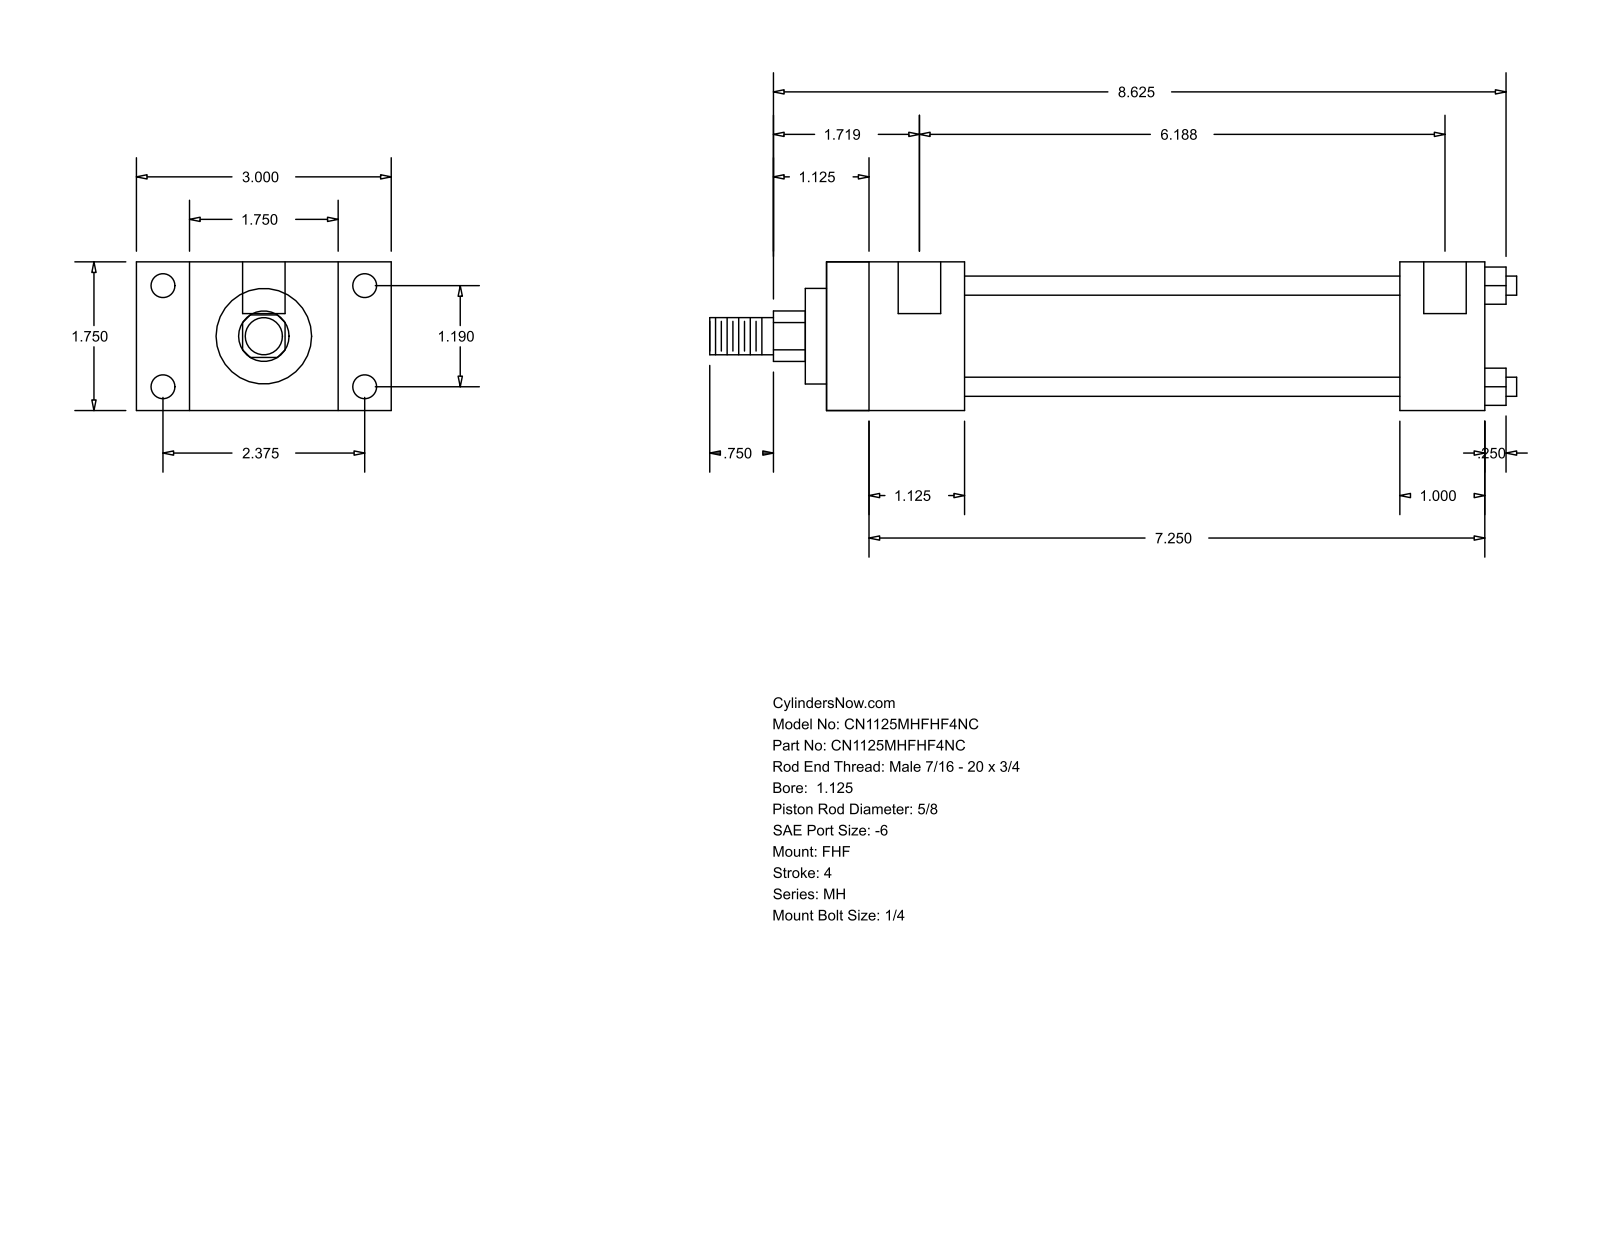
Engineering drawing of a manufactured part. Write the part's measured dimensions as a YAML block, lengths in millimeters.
part_name: "MH_FHF__0112_0.625"
step_written_by: "GSSL Pune (CONFIG_CONTROL_DESIGN)"
units: millimeters
bodies: {solids: 0, faces: 88, planar: 60, cylindrical: 28, other: 0}
overall_size: [241.3, 76.2, 44.45]
round_holes:
  - {diameter: 5.56, count: 4}
  - {diameter: 7.14, count: 4}
  - {diameter: 12.7, count: 2}
round_bosses_or_shafts:
  - {diameter: 5.71, count: 4}
  - {diameter: 34.92, count: 1}
  - {diameter: 28.57, count: 1}
  - {diameter: 15.88, count: 1}
  - {diameter: 11.11, count: 1}
partial_cylinders:
  - {radius: 7.54, count: 1}
face_to_face_distances: [44.46, 15.87, 60.33, 41.27, 76.2, 196.84, 155.57, 25.4, 171.44, 130.17]
hole_center_spacings: [30.22, 60.32, 67.47, 153.99, 3.17, 157.16]
